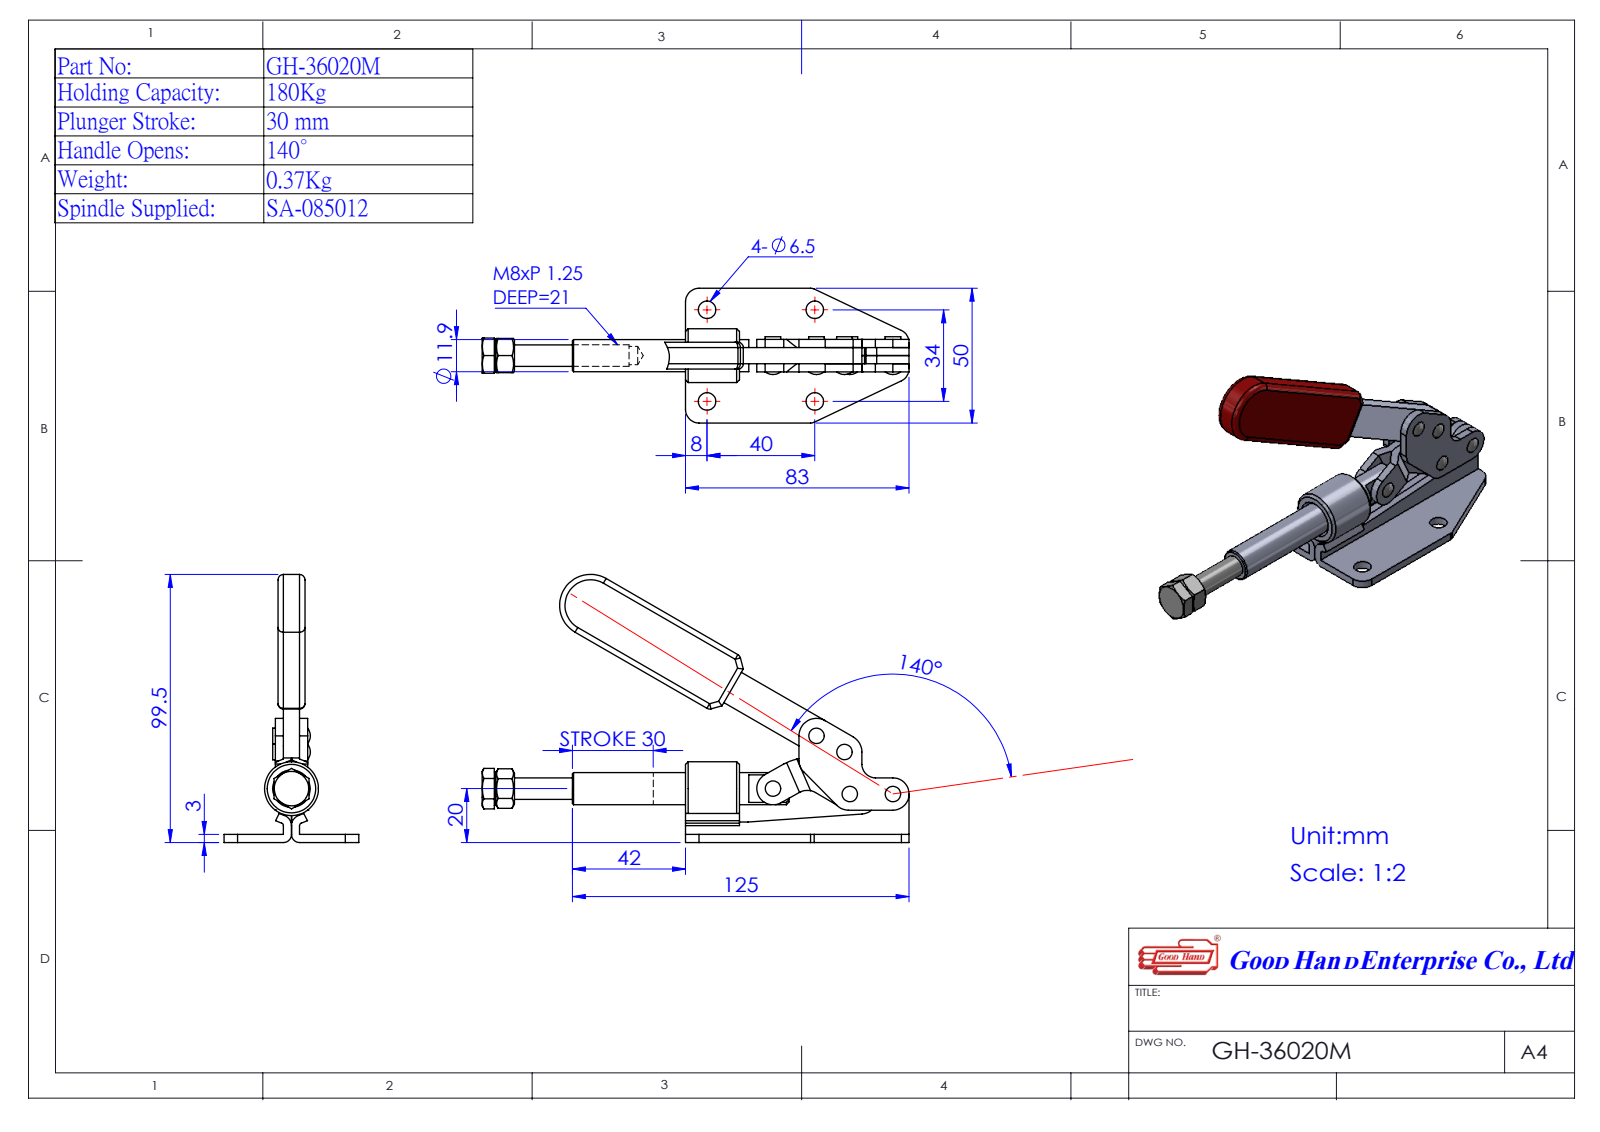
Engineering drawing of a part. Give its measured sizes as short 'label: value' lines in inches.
name: 43602033-1^GH-36020M(簡化); GH-36020M(簡化); Group2^GH-36020M(簡化); Group1^GH-36020M(簡化) (+2 more)
written by: SolidWorks 2016 (AUTOMOTIVE_DESIGN)
unit: in
bodies: 6 solids, 217 faces (108 planar, 85 cylindrical, 24 other)
size: 6.24 × 3.917 × 1.969
volume: 3.516 in³; area: 46.32 in²
holes: 4× ⌀0.256, 3× ⌀0.157, 1× ⌀0.268, 1× ⌀0.315, 1× ⌀0.469
bosses: 5× ⌀0.228, 1× ⌀0.787, 1× ⌀0.492
rounds: 7× R0.236, 3× R0.197, 2× R0.039, 2× R0.157, 2× R0.256, 1× R0.453, 1× R0.709
face distances: 0.118, 0.079, 0.315, 0.236, 0.039, 0.354, 0.394, 0.433, 0.472, 0.709
hole spacings: 1.339, 1.575, 2.067, 0.63, 1.126, 1.755
